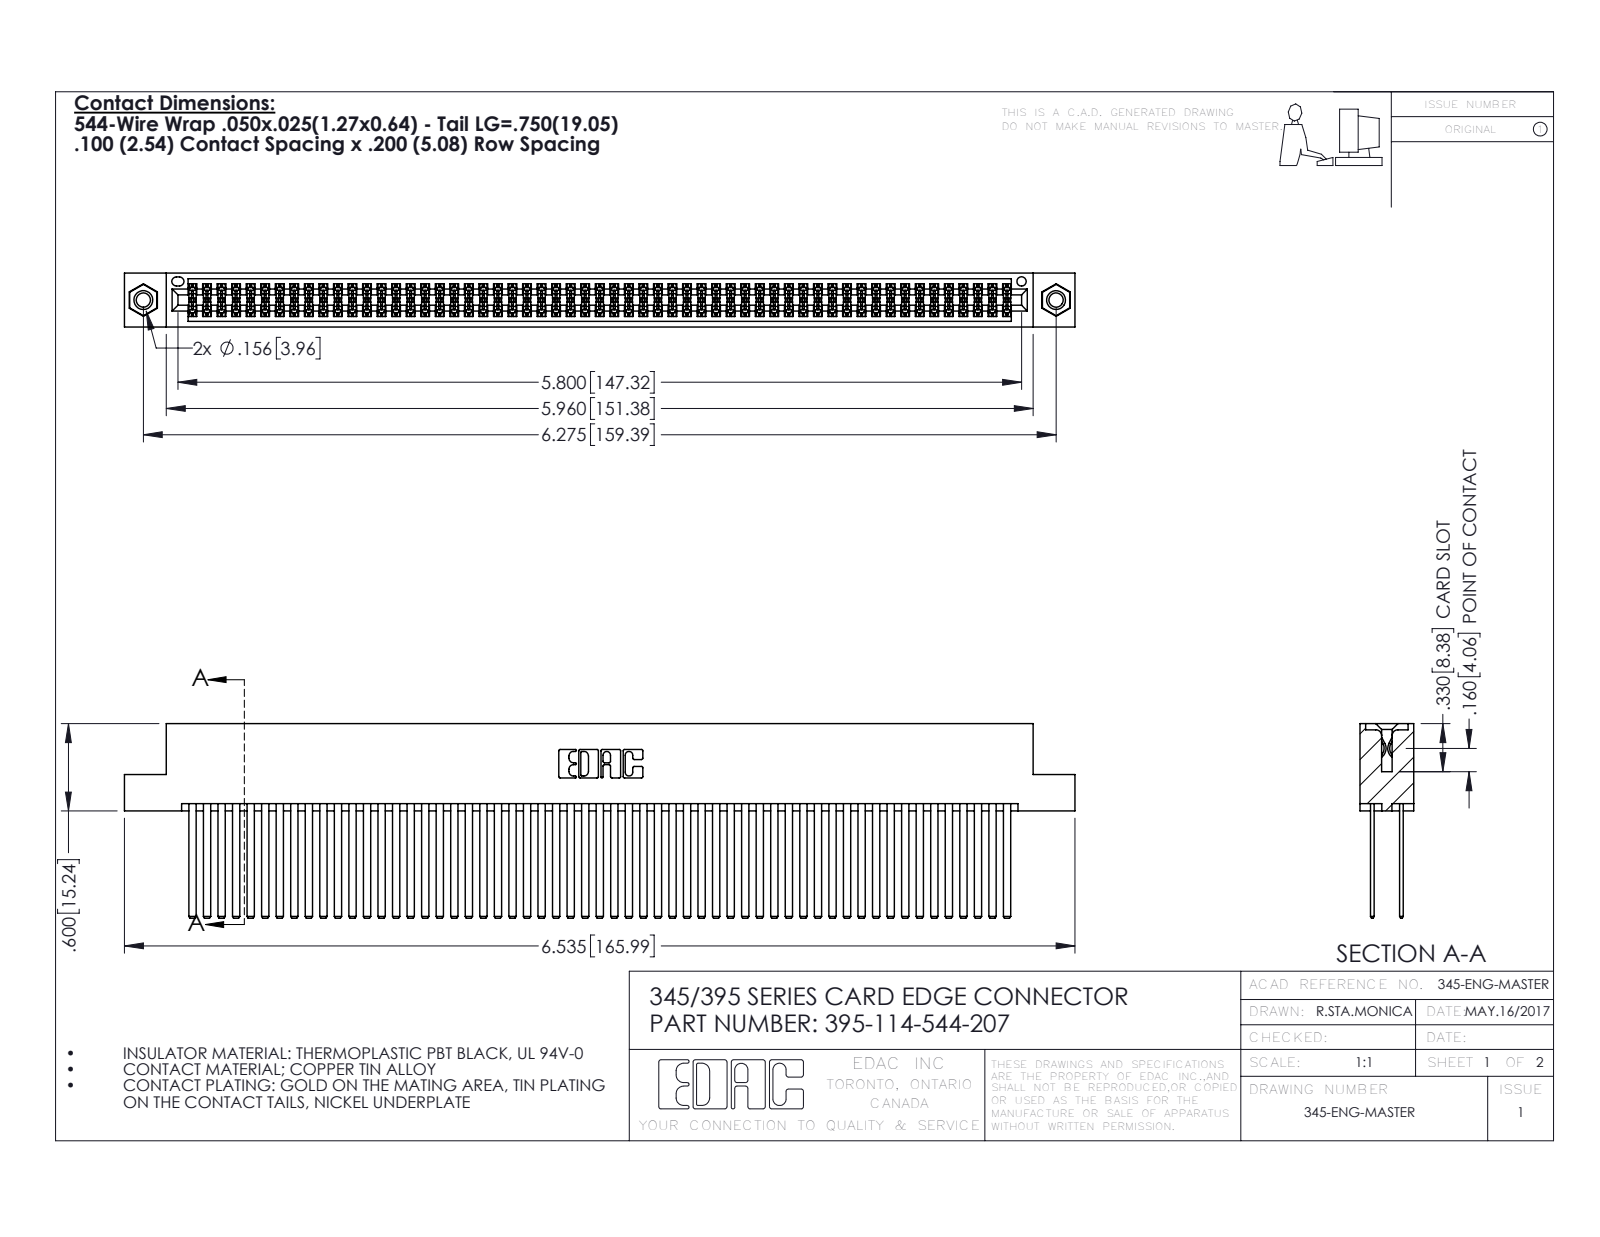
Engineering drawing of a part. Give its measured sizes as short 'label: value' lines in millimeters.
name: 345 Part_Flush Mounting Lugs - 0.156 Dia-TI; 345-250-001_345-250-005-103; 345-292-001_345-293-144; 395-114-544-207
written by: SolidWorks 2016 (CONFIG_CONTROL_DESIGN)
unit: mm
bodies: 117 solids, 5202 faces (3418 planar, 1768 cylindrical, 16 other)
size: 166 × 34 × 9.4
volume: 17 850 mm³; area: 31 390 mm²
holes: 2× ⌀2.5, 2× ⌀3.2, 2× ⌀4, 1× ⌀1.6
bosses: 2× ⌀3.9
rounds: 171× R0.2, 22× R0.3, 6× R0.2, 6× R0.8, 3× R0.7, 2× R0.4, 2× R0.5, 2× R0.6
face distances: 5.1, 0.6, 1.8, 2.5, 6.9, 7.6, 5.7, 4.4, 9.4, 1.3
hole spacings: 6.9, 153.4, 159.4
